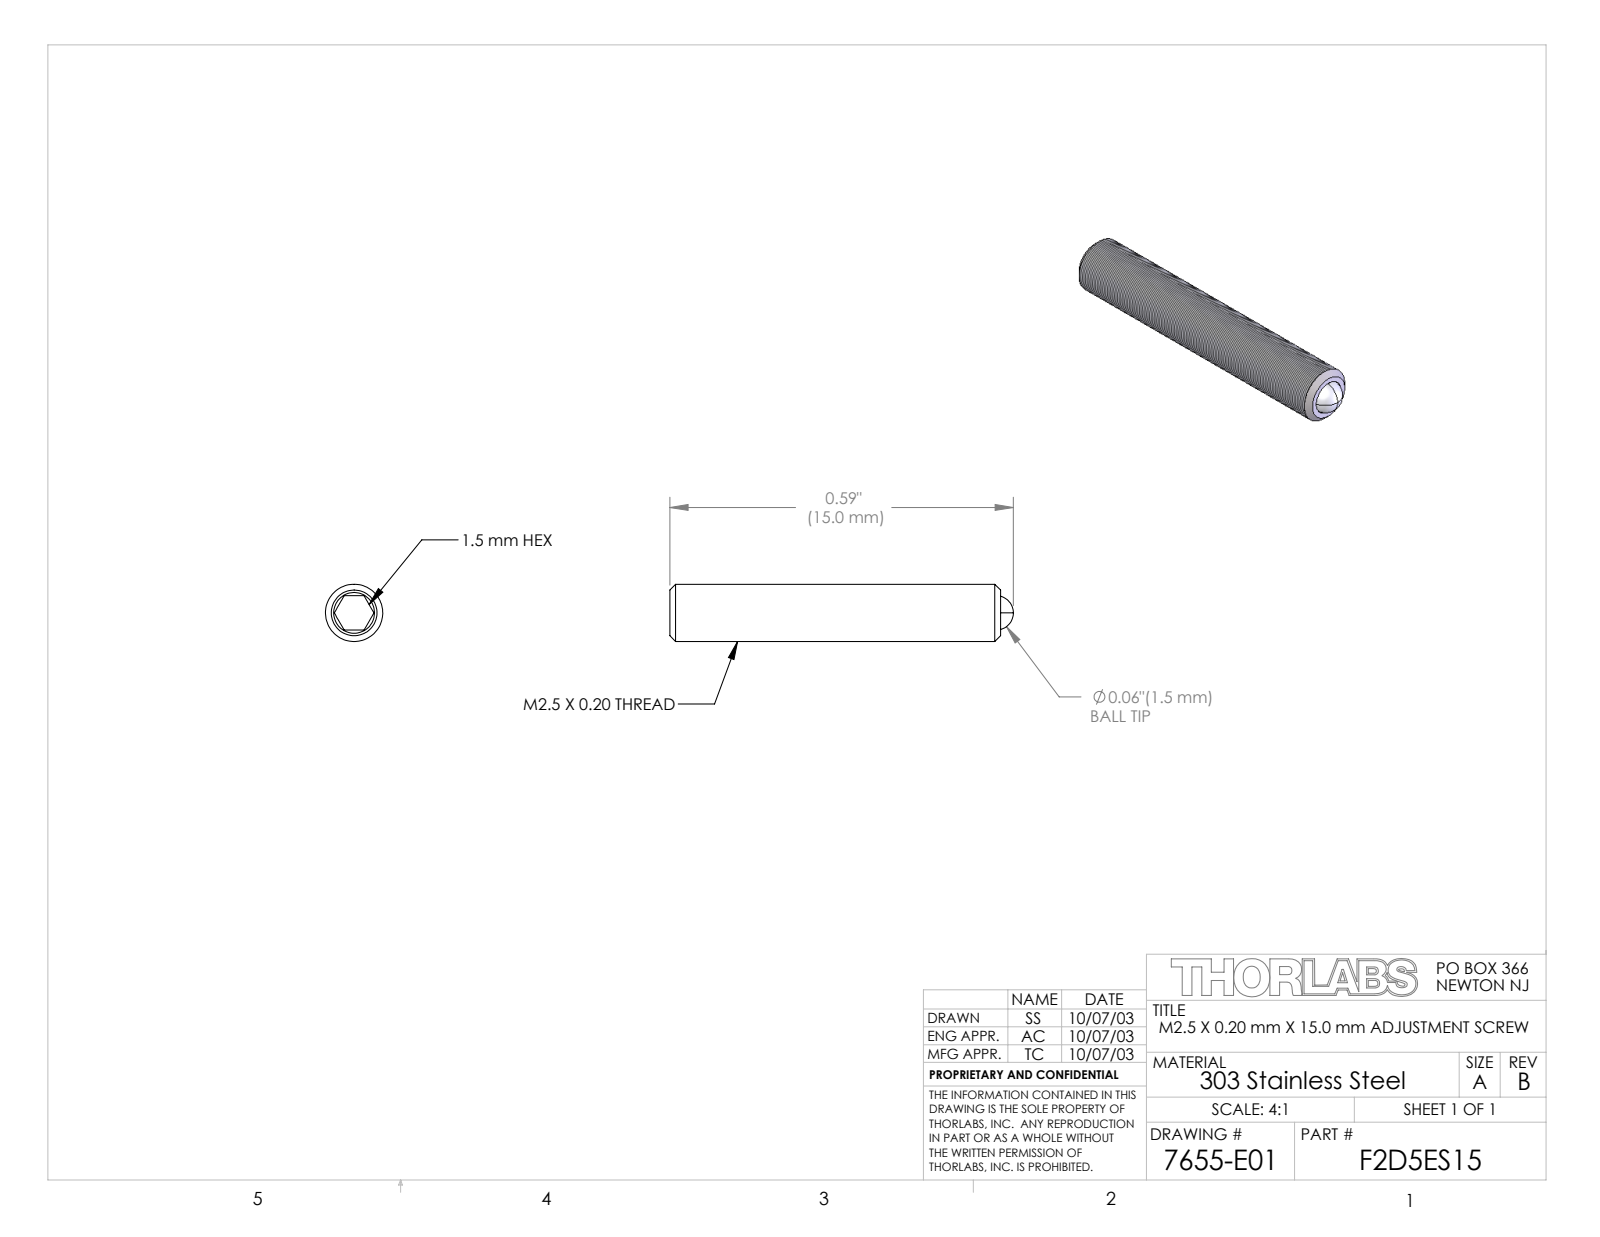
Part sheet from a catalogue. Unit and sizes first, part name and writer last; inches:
Units: inches
Overall size (bounding box): 0.613 × 0.098 × 0.098
Round holes (diameter × count): ⌀0.059 ×1
Round bosses / shafts (diameter × count): ⌀0.098 ×1
Main face-to-face distances: 0.059, 0.47, 0.591, 0.12
Volume: 0.004 in³ · Surface area: 0.234 in²
Bodies: 2 solids, 25 faces (9 planar, 4 cylindrical, 12 other)
Part name (STEP PRODUCT): 7655-E0W
STEP written by: SolidWorks 2011 (AUTOMOTIVE_DESIGN)
